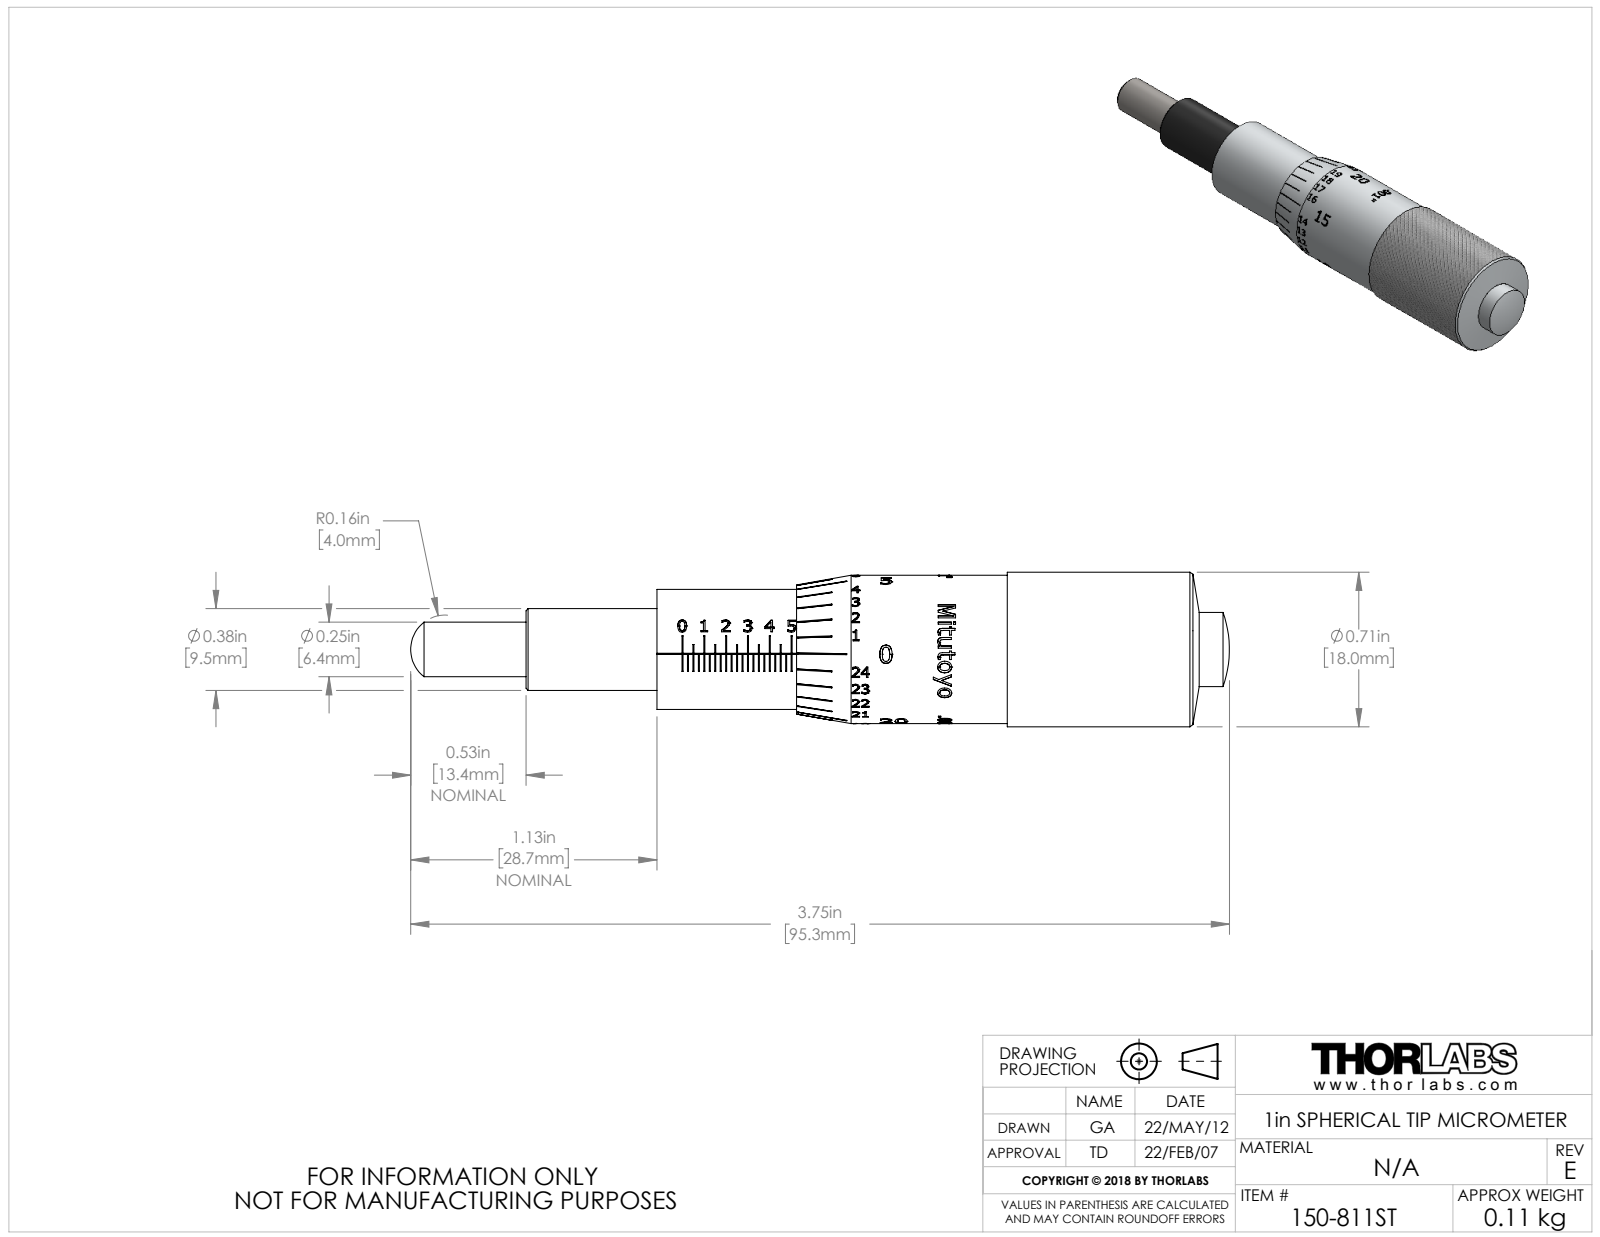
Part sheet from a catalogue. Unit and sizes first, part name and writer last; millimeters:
Units: millimetres
Overall size (bounding box): 95.32 × 18 × 18
Round holes (diameter × count): ⌀6.35 ×1
Round bosses / shafts (diameter × count): ⌀18 ×1, ⌀17.27 ×1, ⌀13.97 ×1, ⌀11.18 ×1, ⌀9.53 ×1, ⌀8.64 ×1
Partial cylindrical surfaces — rounded edges, fillets, slot ends (radius × count): R6.97 ×1, R7.54 ×1, R8.23 ×1, R8.53 ×1, R8.62 ×1
Main face-to-face distances: 53.71, 39.37, 14.34, 30.99, 8.38, 22.72, 15.24, 46.23, 54.61, 68.95
Volume: 13 119 mm³ · Surface area: 9 762 mm²
Bodies: 2 solids, 1487 faces (738 planar, 169 cylindrical, 580 other)
Part name (STEP PRODUCT): 13432-E0W
STEP written by: SolidWorks 2016 (AUTOMOTIVE_DESIGN)
